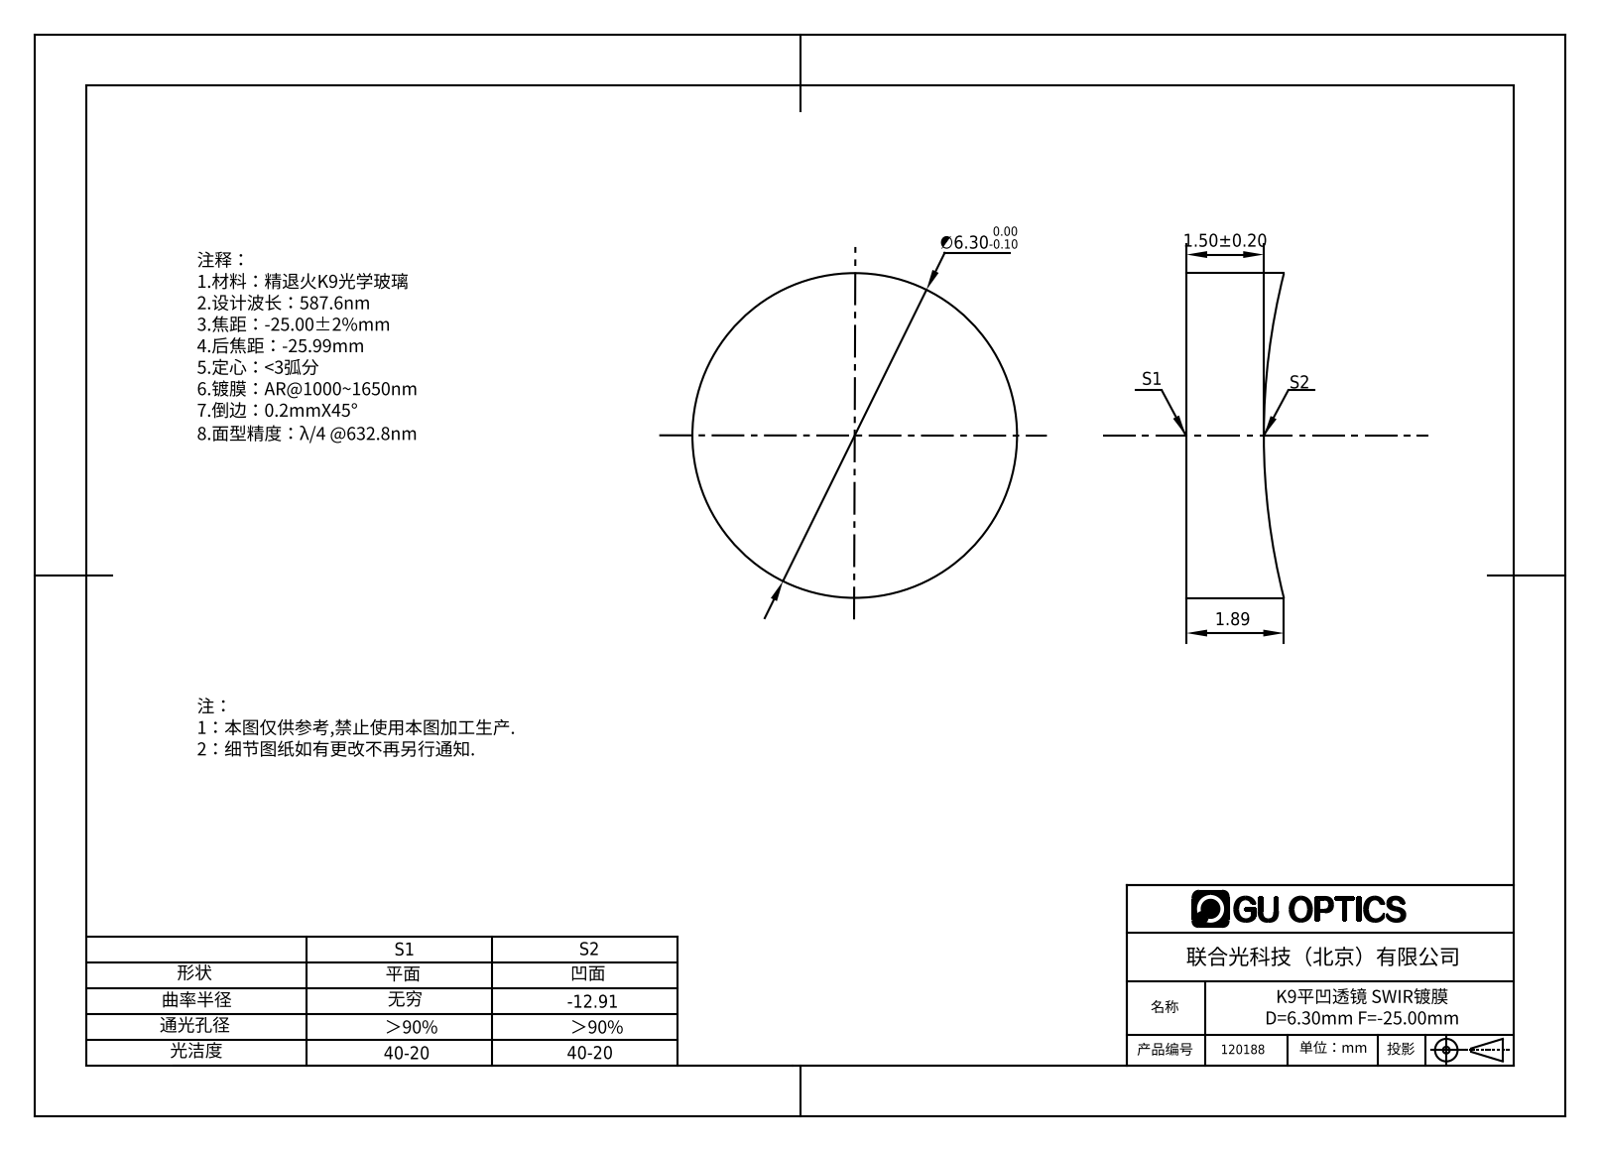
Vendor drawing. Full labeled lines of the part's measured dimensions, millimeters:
Part name (STEP PRODUCT): 120128
STEP written by: SolidWorks 2016 (AUTOMOTIVE_DESIGN)
Units: millimetres
Bodies: 1 solid, 5 faces (1 planar, 2 cylindrical, 2 other)
Overall size (bounding box): 6.3 × 6.3 × 1.89
Volume: 53 mm³ · Surface area: 100 mm²
Round bosses / shafts (diameter × count): ⌀6.3 ×1
